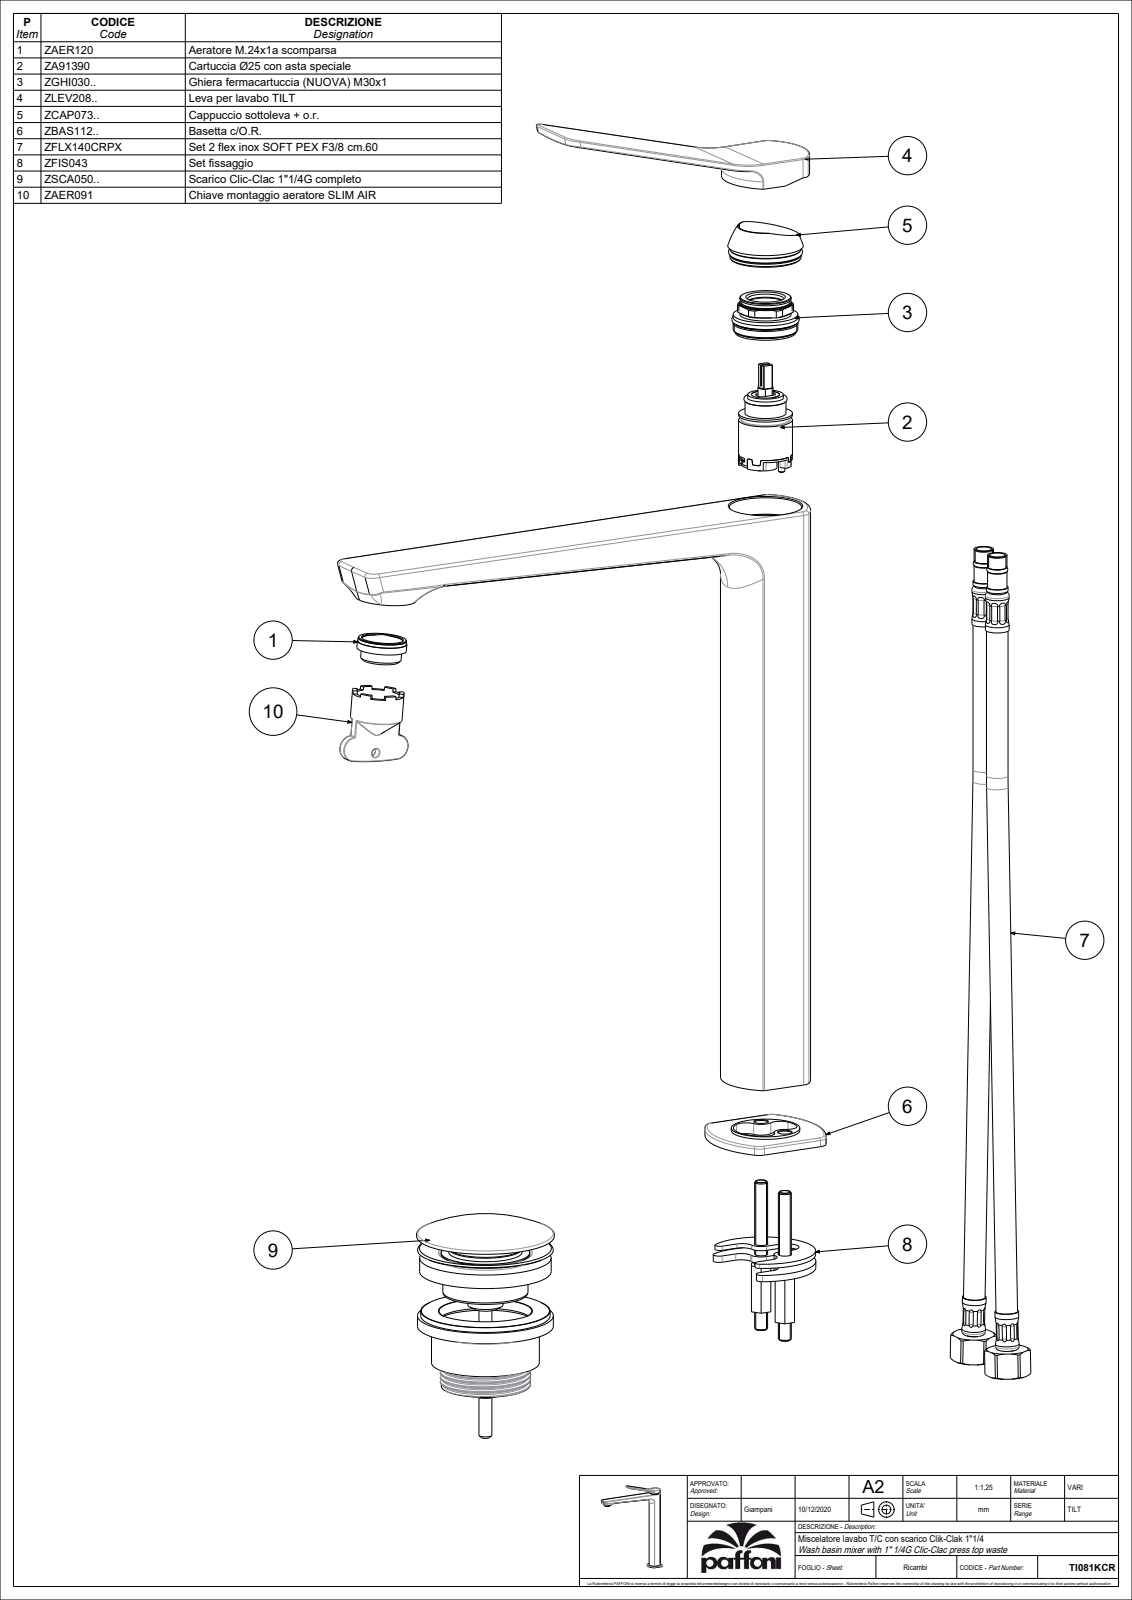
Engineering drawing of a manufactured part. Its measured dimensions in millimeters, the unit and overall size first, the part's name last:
Units: millimetres
Overall size (bounding box): 318.81 × 247.97 × 50
Round holes (diameter × count): ⌀5 ×2, ⌀6.2 ×2, ⌀4 ×1, ⌀4.2 ×1, ⌀5.5 ×1, ⌀16 ×1, ⌀19.5 ×1, ⌀26.5 ×1, ⌀28 ×1, ⌀29 ×1, ⌀30.6 ×1, ⌀33.5 ×1
Round bosses / shafts (diameter × count): ⌀41 ×1, ⌀33 ×1, ⌀31.8 ×1, ⌀30.3 ×1, ⌀18.8 ×1, ⌀9.5 ×1, ⌀6.2 ×1, ⌀5.4 ×1
Partial cylindrical surfaces — rounded edges, fillets, slot ends (radius × count): R2.17 ×26, R1.68 ×24, R5 ×18, R0.5 ×15, R1 ×8, R1.4 ×4, R1.48 ×4, R21.06 ×2
Main face-to-face distances: 3.98, 279, 3.94, 1.5, 293.5, 14.5, 288, 275, 13, 4
Hole centre spacings: 11.7, 13.04, 11, 22
Volume: 235 418 mm³ · Surface area: 121 838 mm²
Bodies: 2 solids, 643 faces (125 planar, 190 cylindrical, 328 other)
Part name (STEP PRODUCT): TI081CR
STEP written by: CREO PARAMETRIC BY PTC INC, 2020044 (CONFIG_CONTROL_DESIGN)
